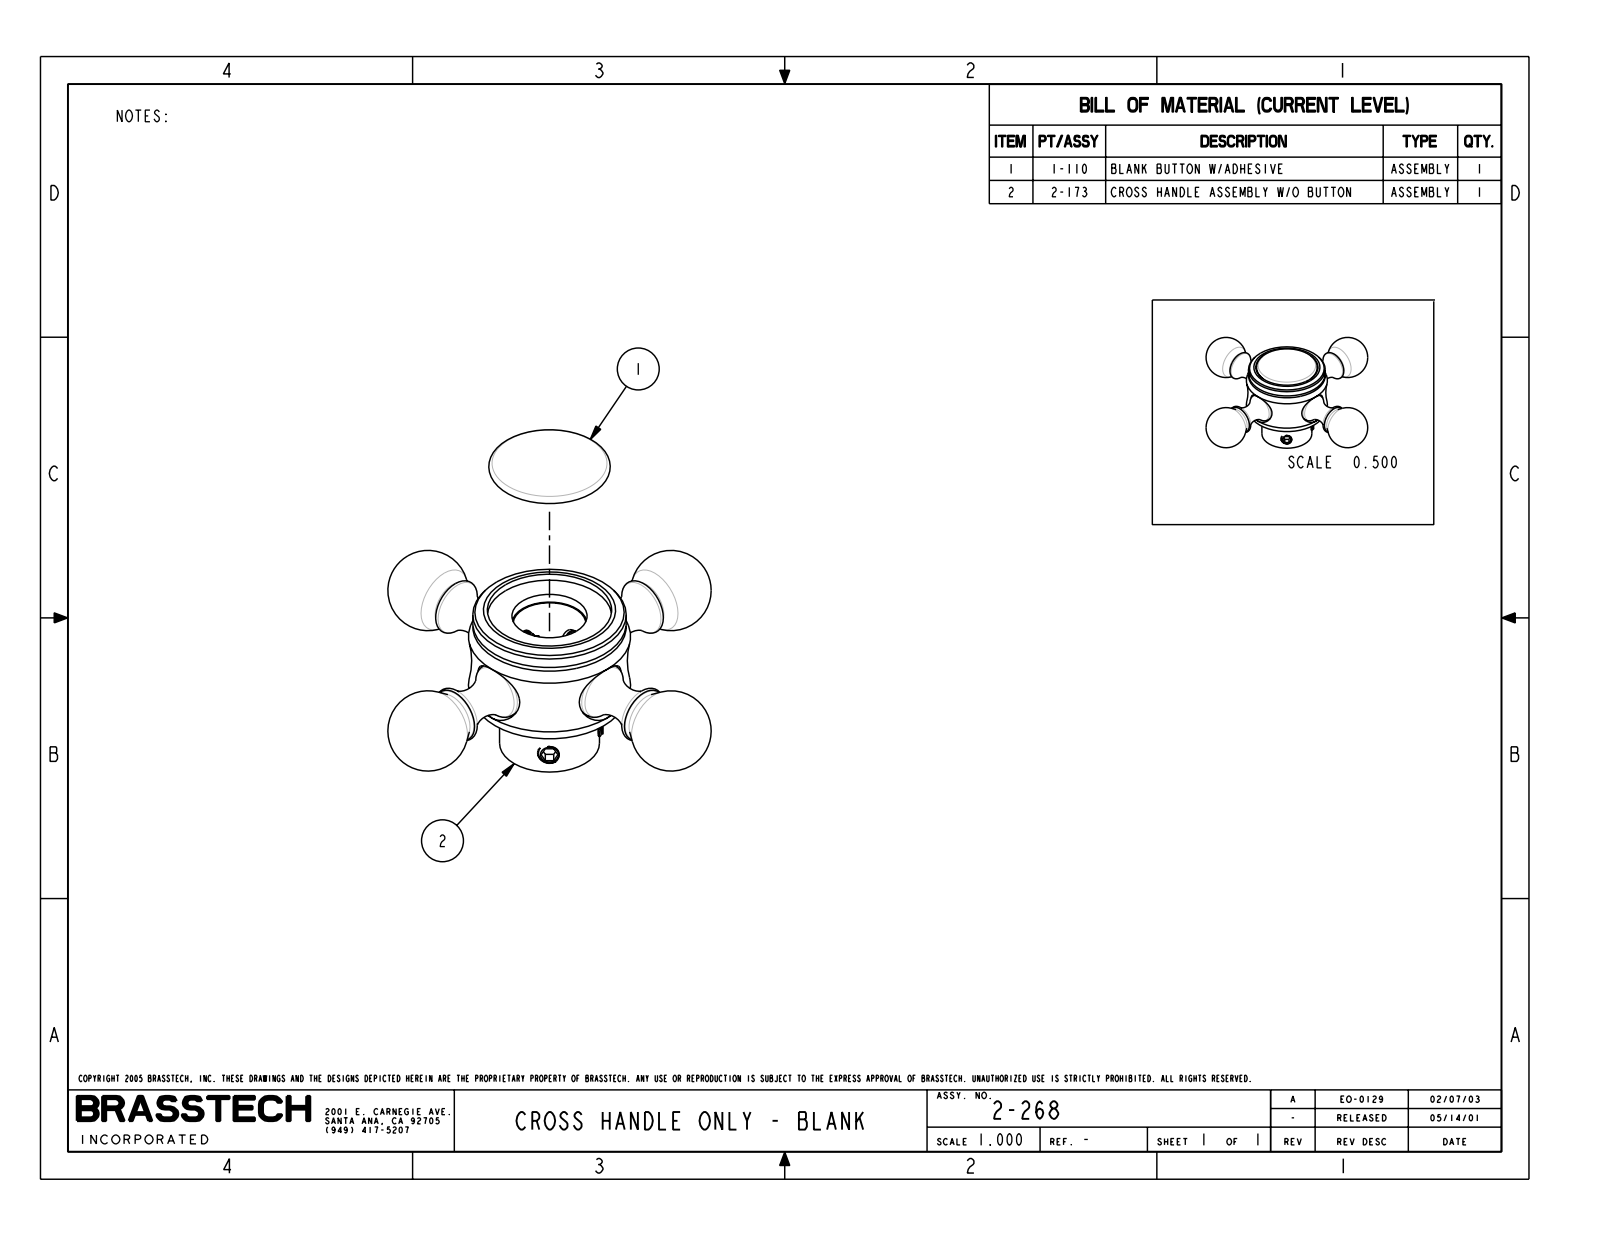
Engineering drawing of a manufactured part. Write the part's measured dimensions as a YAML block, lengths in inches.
part_name: "10135; 10136; 92000; 2-173_ASM (+4 more)"
step_written_by: "CREO PARAMETRIC BY PTC INC, 2018400 (CONFIG_CONTROL_DESIGN)"
units: inches
bodies: {solids: 9, faces: 648, planar: 122, cylindrical: 194, other: 332}
overall_size: [2.915, 2.915, 1.195]
volume: 1.106
surface_area: 27.37
round_holes:
  - {diameter: 0.13, count: 2}
  - {diameter: 0.206, count: 2}
  - {diameter: 0.41, count: 2}
  - {diameter: 0.5, count: 1}
  - {diameter: 0.517, count: 1}
  - {diameter: 0.855, count: 1}
round_bosses_or_shafts:
  - {diameter: 0.392, count: 2}
  - {diameter: 0.25, count: 2}
  - {diameter: 0.18, count: 2}
  - {diameter: 0.164, count: 2}
  - {diameter: 1.055, count: 1}
  - {diameter: 0.687, count: 1}
partial_cylinders:
  - {radius: 0.169, count: 1}
  - {radius: 0.187, count: 1}
face_to_face_distances: [0.965, 1.07, 0.21, 0.755, 1.065, 0.05, 1.12, 0.055, 0.359, 0.706]
